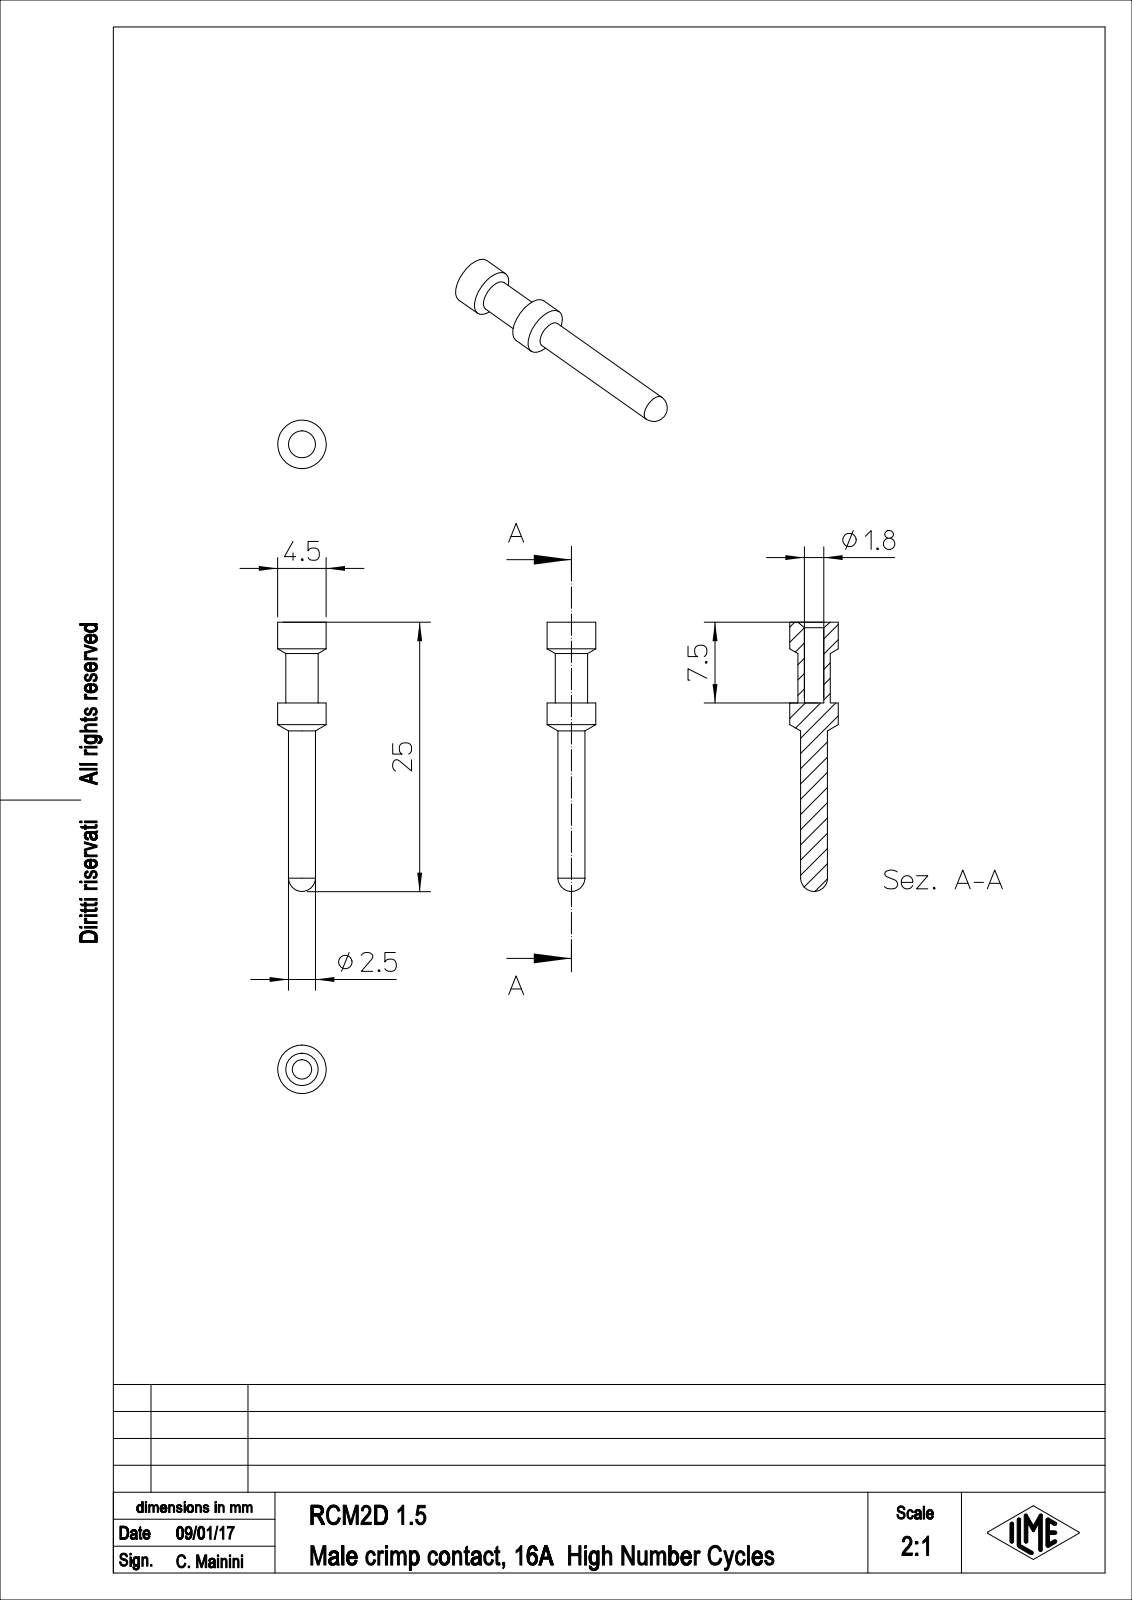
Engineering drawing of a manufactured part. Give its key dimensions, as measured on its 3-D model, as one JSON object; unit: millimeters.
{"part_name": "RCM2D_1.5", "step_written_by": "PTC Creo Elements/Direct Modeling 19.0E 27-Jun-2016 (C) Parametric Technology GmbH (AUTOMOTIVE_DESIGN)", "units": "millimeters", "bodies": {"solids": 1, "faces": 21, "planar": 3, "cylindrical": 10, "other": 8}, "overall_size": [25, 4.5, 4.5], "volume_mm3": 165, "surface_area_mm2": 312, "round_holes": [[1.8, 1]], "round_bosses_or_shafts": [[4.5, 1], [3, 1], [2.5, 1]], "face_to_face_distances": [7.5]}
